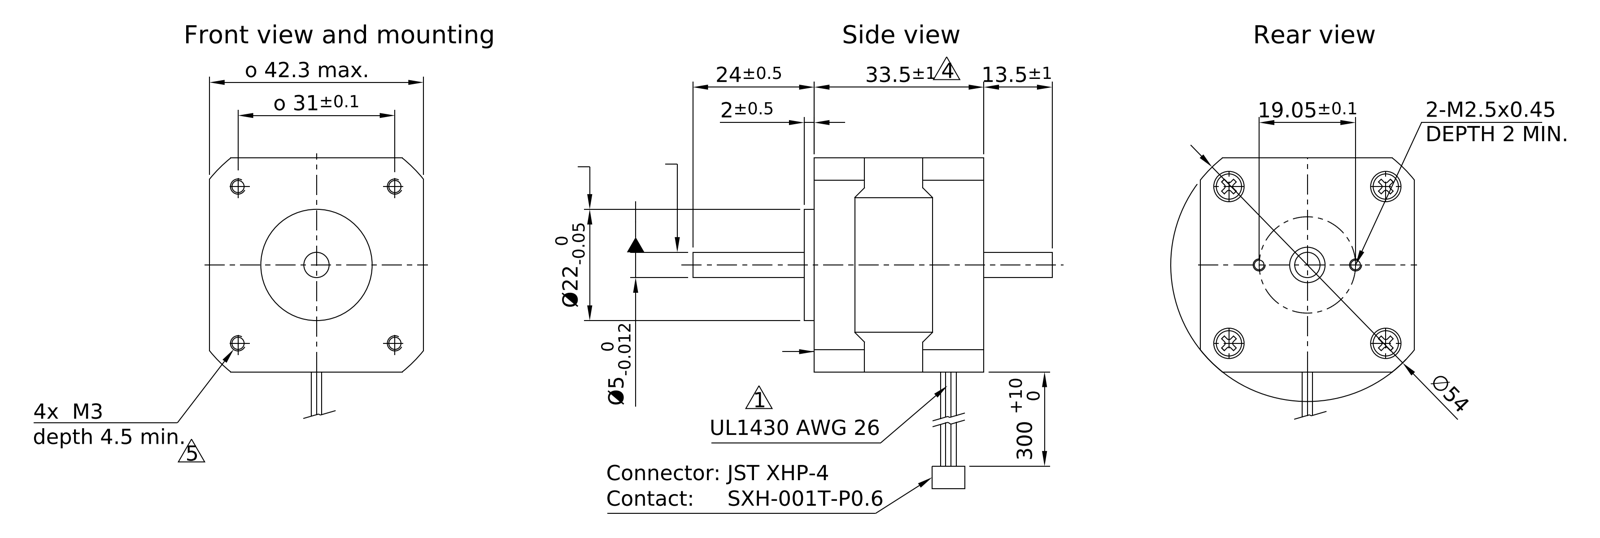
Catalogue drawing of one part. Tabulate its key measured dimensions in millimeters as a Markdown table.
| quantity | value |
| --- | --- |
| part name | ST4209S...-B |
| STEP written by | Autodesk Inventor 2017 (AUTOMOTIVE_DESIGN) |
| units | millimeters |
| bodies | 15 solids, 197 faces (98 planar, 72 cylindrical, 27 other) |
| overall size | 71 × 54 × 42 |
| volume | 58 097 mm³ |
| surface area | 18 027 mm² |
| round holes (diameter × count) | 1 × 6, 2.46 × 4, 2.7 × 4, 6 × 4, 2.01 × 2, 7 × 1, 10 × 1 |
| round bosses / shafts (diameter × count) | 2.5 × 4, 2.22 × 4, 22 × 1, 5 × 1 |
| partial cylindrical surfaces (radius × count) | 2 × 8, 27 × 1 |
| main face-to-face distances | 16.3, 42, 9, 25.3, 33.5, 24.5, 8.2, 2, 10.2, 48.08 |
| hole center spacings | 1, 1.41, 16.61, 21.92, 29.44, 31, 2, 2.24 |
